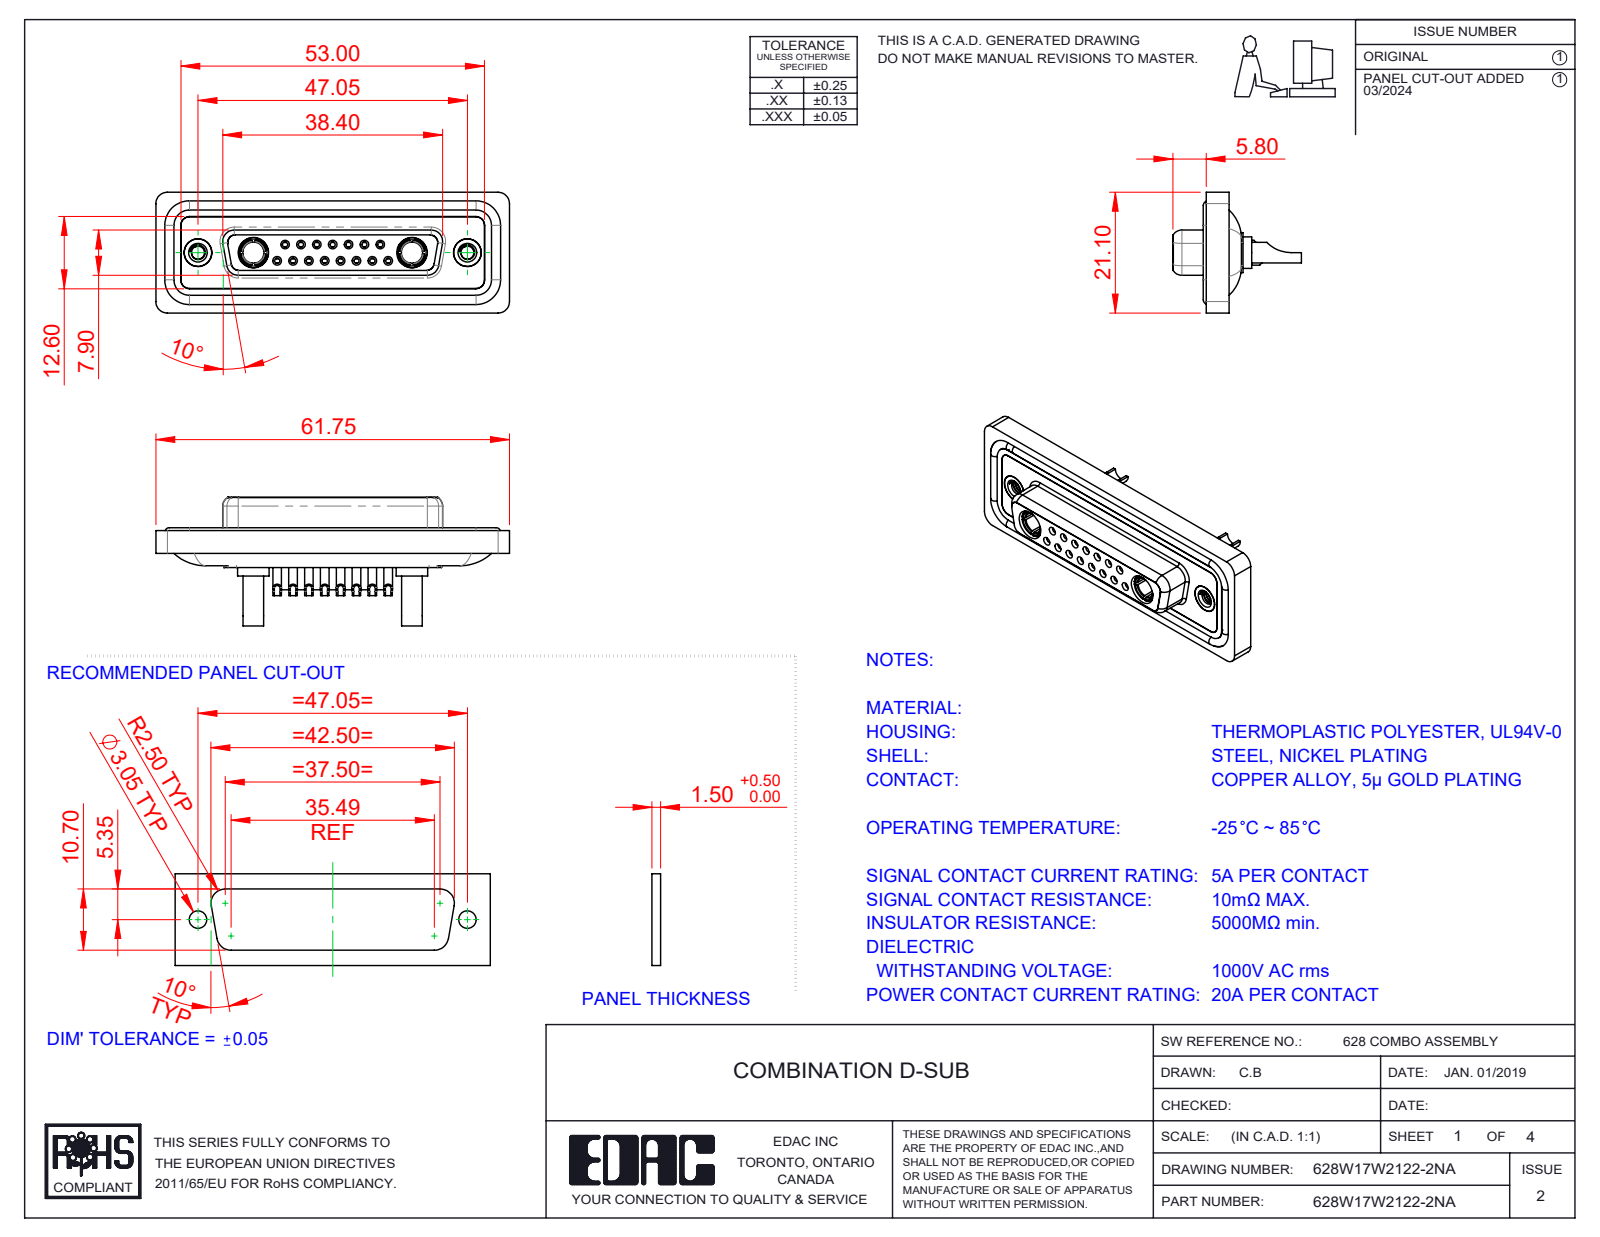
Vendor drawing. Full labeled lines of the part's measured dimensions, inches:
Part name (STEP PRODUCT): 628Combo Contact Row 1_22; 628Combo Contact Row 2_22; 628W17W2122-2NA; 628Combo Threaded Rivet_A (+5 more)
STEP written by: SolidWorks 2023 (CONFIG_CONTROL_DESIGN)
Units: inches
Bodies: 26 solids, 1369 faces (424 planar, 557 cylindrical, 388 other)
Overall size (bounding box): 2.431 × 0.884 × 0.831
Volume: 0.512 in³ · Surface area: 21.98 in²
Round holes (diameter × count): ⌀0.035 ×15, ⌀0.039 ×15, ⌀0.043 ×15, ⌀0.059 ×15, ⌀0.079 ×15, ⌀0.063 ×8, ⌀0.067 ×7, ⌀0.191 ×4, ⌀0.089 ×2, ⌀0.106 ×2, ⌀0.146 ×2, ⌀0.157 ×2
Round bosses / shafts (diameter × count): ⌀0.087 ×15, ⌀0.063 ×11, ⌀0.217 ×2, ⌀0.205 ×2, ⌀0.195 ×2, ⌀0.195 ×2, ⌀0.189 ×2, ⌀0.187 ×2
Partial cylindrical surfaces — rounded edges, fillets, slot ends (radius × count): R0.059 ×22, R0.079 ×18, R0.053 ×8, R0.063 ×8, R0.039 ×6, R0.01 ×4, R0.02 ×4, R0.024 ×4
Main face-to-face distances: 0.016, 0.071, 0.293, 0.222, 0.26, 0.02, 0.278, 0.063, 0.114, 0.043
Hole centre spacings: 0.124, 0.109, 0.327, 0.218, 0.198, 0.198, 0.295, 0.436
